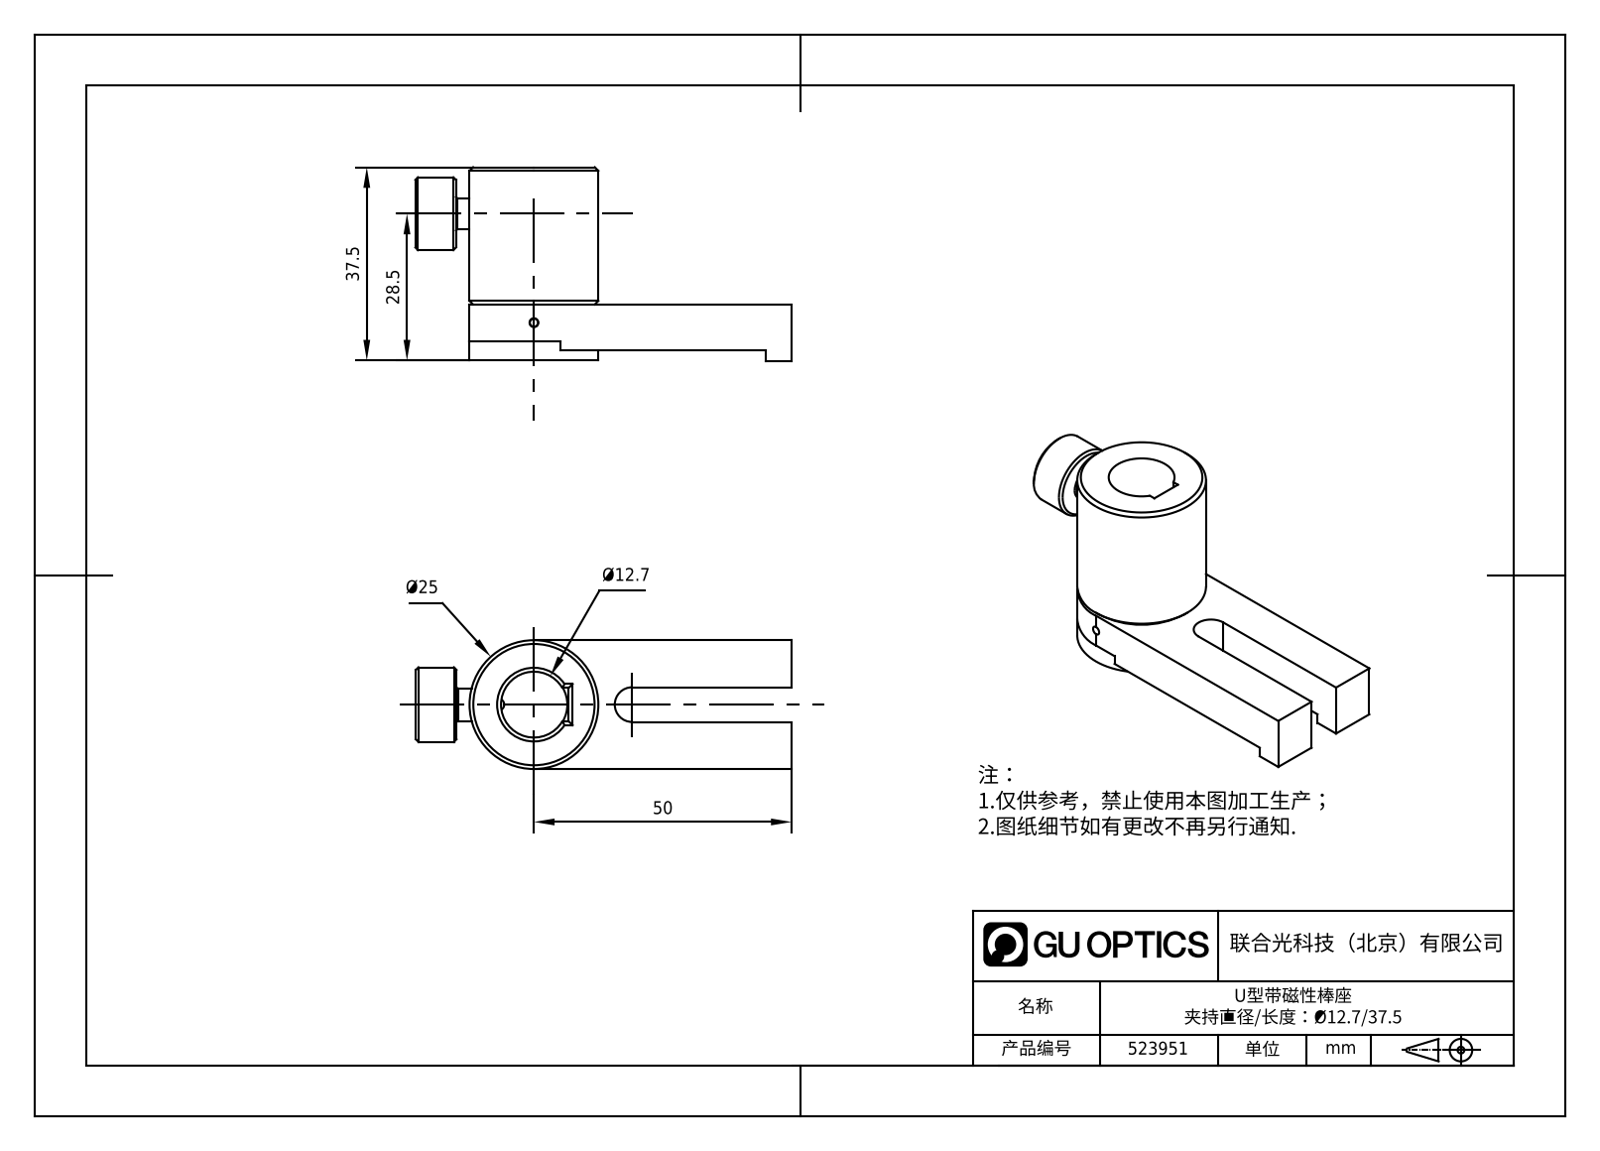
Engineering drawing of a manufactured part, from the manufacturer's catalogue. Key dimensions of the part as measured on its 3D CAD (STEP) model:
Part name (STEP PRODUCT): 523951
STEP written by: SolidWorks 2016 (CONFIG_CONTROL_DESIGN)
Units: millimetres
Bodies: 7 solids, 120 faces (36 planar, 46 cylindrical, 38 other)
Overall size (bounding box): 73 × 37.55 × 24.99
Volume: 22 431 mm³ · Surface area: 12 080 mm²
Round holes (diameter × count): ⌀4.83 ×3, ⌀1.59 ×1, ⌀1.7 ×1, ⌀1.78 ×1, ⌀12.78 ×1, ⌀12.95 ×1, ⌀20.09 ×1
Round bosses / shafts (diameter × count): ⌀4.76 ×3, ⌀24.99 ×1, ⌀20.05 ×1, ⌀17.78 ×1, ⌀17.27 ×1, ⌀14.12 ×1, ⌀5.99 ×1
Partial cylindrical surfaces — rounded edges, fillets, slot ends (radius × count): R3.37 ×1, R12.95 ×1
Main face-to-face distances: 8.89, 9.13, 15.87, 25, 1.83, 7.06, 1.98, 3.81, 10.87, 37.5
Hole centre spacings: 16.5, 9.53, 9.52
